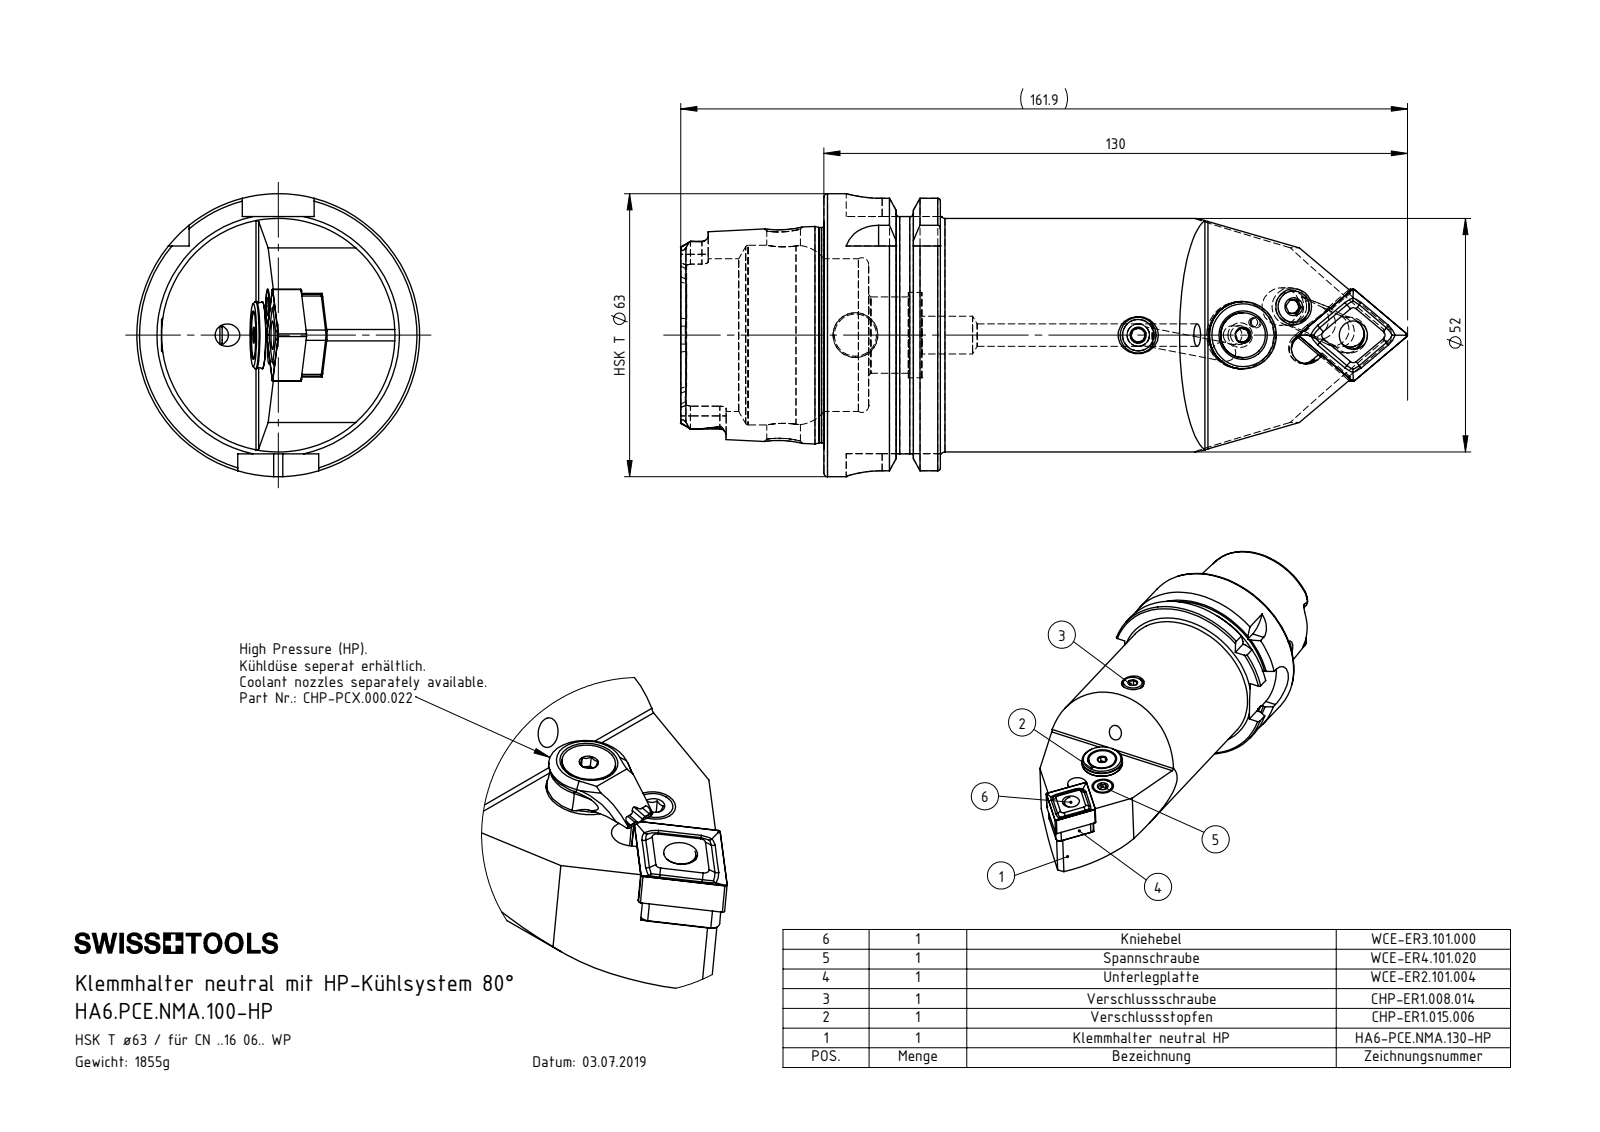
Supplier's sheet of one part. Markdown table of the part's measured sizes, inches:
| quantity | value |
| --- | --- |
| part name | DIN 3771 - 13x1; ISO 8752 2x8; WCE-ER3.101.000_A; HA6-PCE.NMA.100-HP_B (+8 more) |
| STEP written by | SolidWorks 2017 (AUTOMOTIVE_DESIGN) |
| units | inches |
| bodies | 11 solids, 379 faces (160 planar, 87 cylindrical, 132 other) |
| overall size | 5.193 × 2.48 × 2.48 |
| volume | 10.84 in³ |
| surface area | 60.27 in² |
| round holes (diameter × count) | 0.165 × 3, 0.197 × 2, 0.276 × 2, 0.331 × 2, 0.047 × 1, 0.079 × 1, 0.098 × 1, 0.118 × 1, 0.205 × 1, 0.25 × 1, 0.295 × 1, 0.317 × 1 |
| round bosses / shafts (diameter × count) | 0.315 × 2, 2.48 × 1, 2.163 × 1, 2.047 × 1, 1.887 × 1, 0.591 × 1, 0.528 × 1, 0.394 × 1 |
| partial cylindrical surfaces (radius × count) | 0.055 × 6, 0.016 × 4, 0.059 × 4, 0.113 × 4, 0.138 × 4, 0.315 × 4, 0.012 × 2, 0.02 × 2 |
| main face-to-face distances | 1.022, 0.63, 0.392, 1.256, 1.648, 2.278, 0.238, 0.596, 2.079, 1.228 |
| hole center spacings | 0.638, 0.177, 0.178, 0.178, 0.178, 0.581, 0.59, 0.63 |
